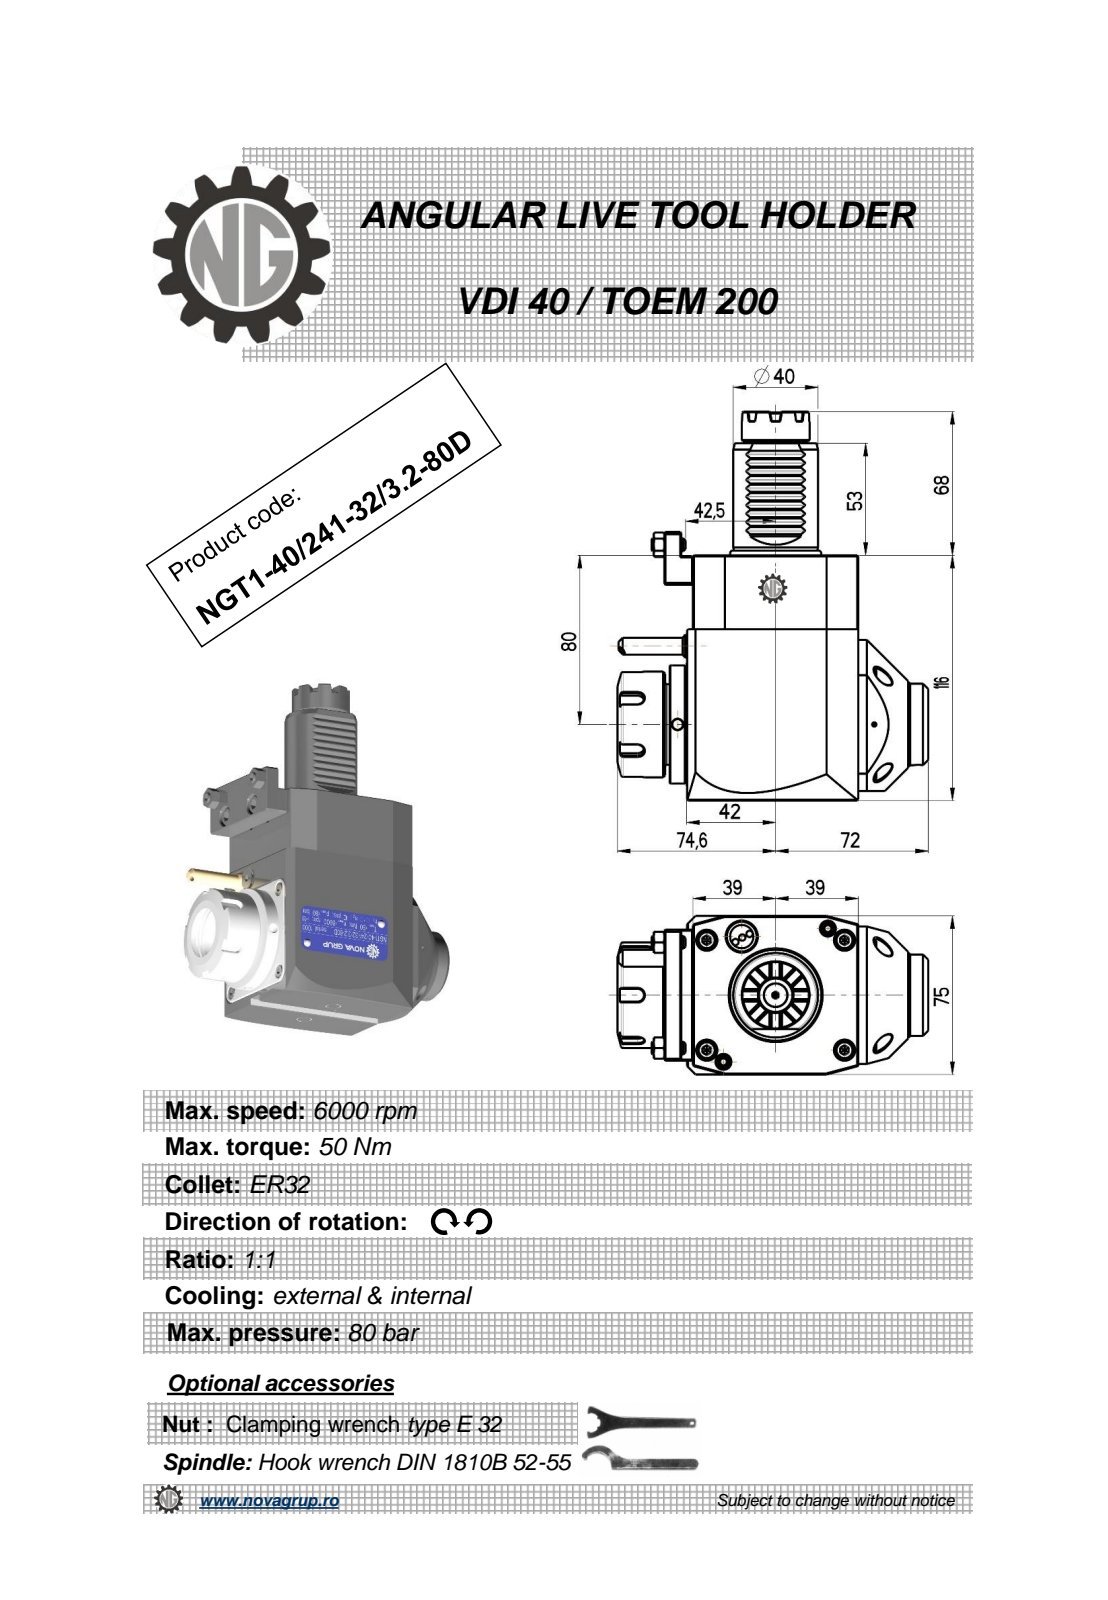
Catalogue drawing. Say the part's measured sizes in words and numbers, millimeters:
The part is named "NGT1_40_241_32_3_2_80D". Its 3-D file was written by "PRO/ENGINEER BY PARAMETRIC TECHNOLOGY CORPORATION, 2010280 (CONFIG_CONTROL_DESIGN)". It is 1 solid with 478 faces: 214 planar, 79 cylindrical and 185 other. Overall it measures 184 by 146.6 by 75 millimeters. Its volume is 917 880 cubic millimeters and its surface area 74 422 square millimeters. Round holes: 3 of diameter 5, 1 of diameter 3, 1 of diameter 27. Round bosses or shafts: 2 of diameter 6, 1 of diameter 56, 1 of diameter 50, 1 of diameter 43, 1 of diameter 40, 1 of diameter 38.5, 1 of diameter 32, 1 of diameter 17.2. Partial cylindrical surfaces (rounded edges, fillets, slot ends): 10 of radius 0.3, 10 of radius 0.31, 6 of radius 0.22, 5 of radius 3, 1 of radius 0.5, 1 of radius 40. The main face-to-face distances are 75, 116, 81, 0.5, 11, 13.5, 8, 2.5, 10.5, 80.8. The hole center spacings are 40.93.
